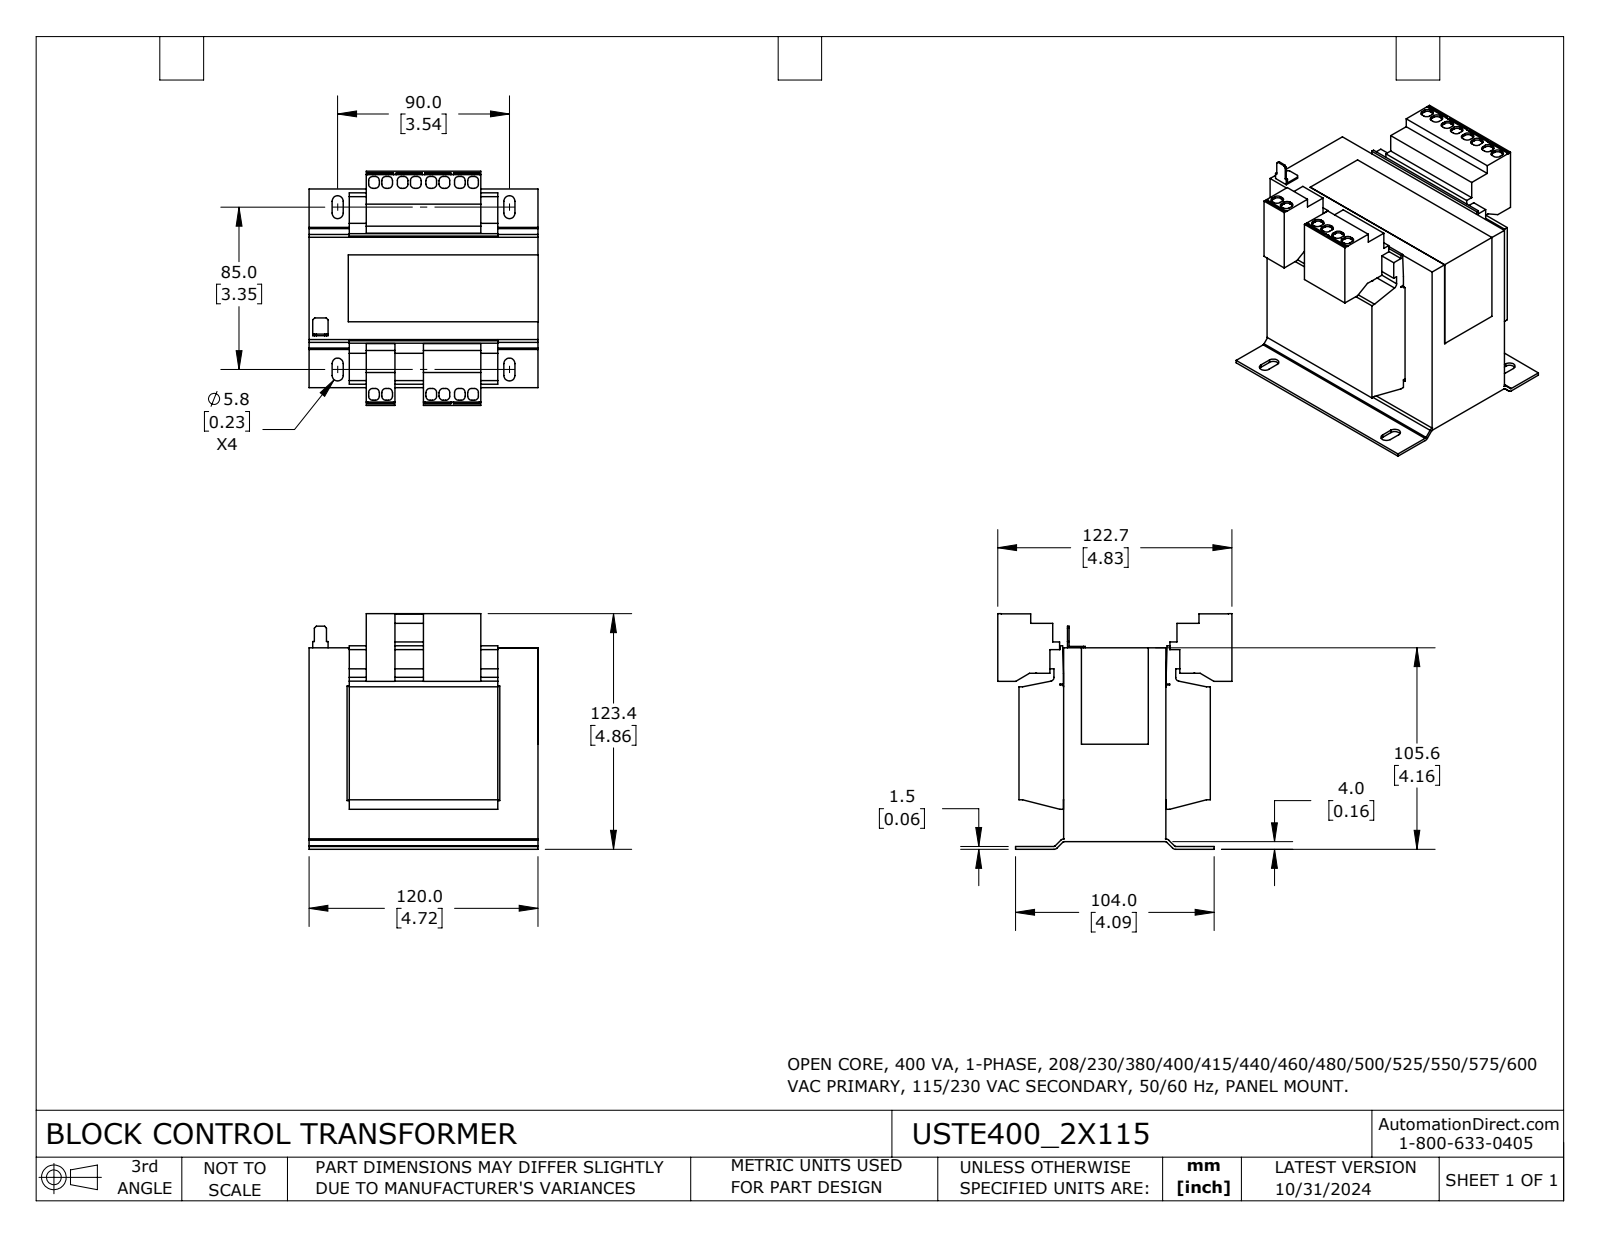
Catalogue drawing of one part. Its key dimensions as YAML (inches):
part_name: "USTE400_2X115"
step_written_by: "SolidWorks 2023 (CONFIG_CONTROL_DESIGN)"
units: inches
bodies: {solids: 1, faces: 434, planar: 356, cylindrical: 78, other: 0}
overall_size: [4.857, 4.831, 4.726]
volume: 59.49
surface_area: 202.4
partial_cylinders:
  - {radius: 0.087, count: 56}
  - {radius: 0.114, count: 8}
  - {radius: 0.039, count: 4}
  - {radius: 0.098, count: 4}
  - {radius: 0.079, count: 2}
face_to_face_distances: [0.833, 3.892, 0.787, 2.109, 1.181, 3.937, 0.045, 3.104, 3.059, 0.059]
